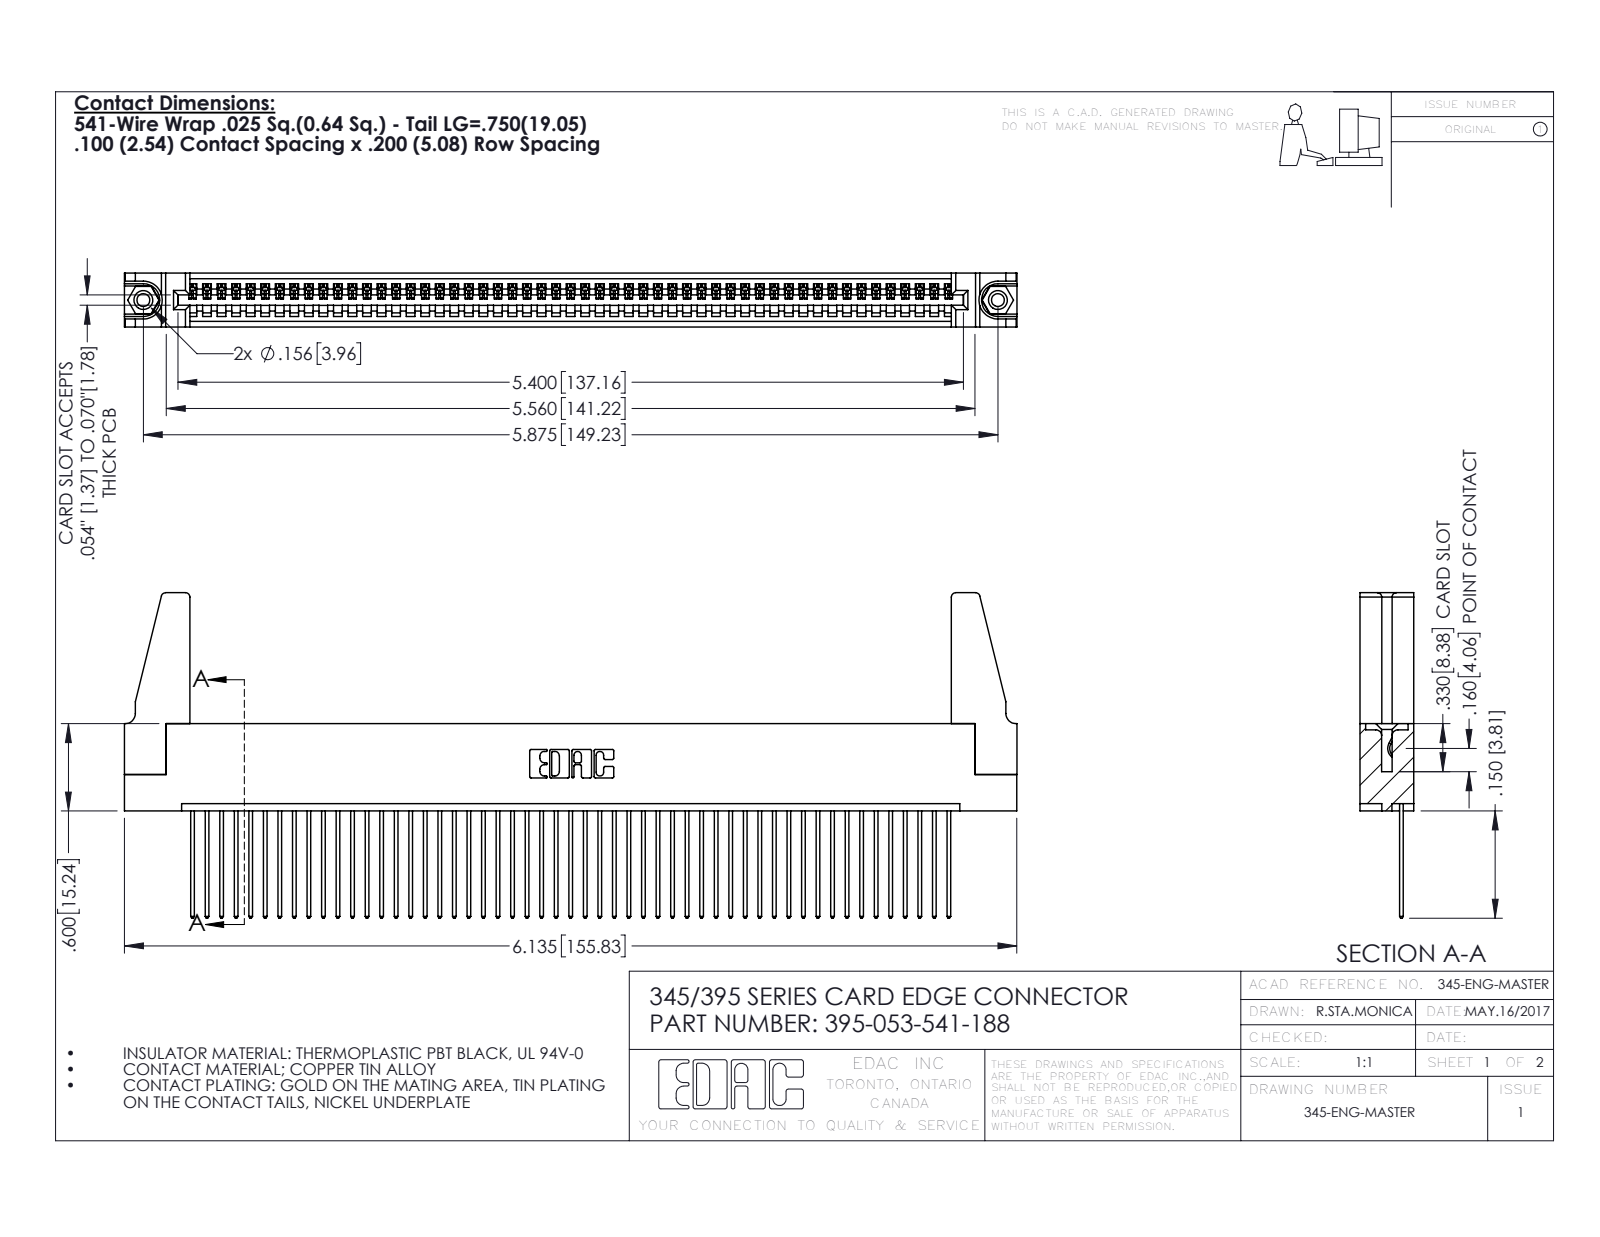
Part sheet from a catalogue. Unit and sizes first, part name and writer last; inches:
Units: inches
Overall size (bounding box): 6.136 × 2.237 × 0.37
Round holes (diameter × count): ⌀0.089 ×2, ⌀0.125 ×2, ⌀0.156 ×2, ⌀0.064 ×1
Round bosses / shafts (diameter × count): ⌀0.155 ×2
Partial cylindrical surfaces — rounded edges, fillets, slot ends (radius × count): R0.006 ×106, R0.01 ×106, R0.01 ×22, R0.03 ×8, R0.007 ×6, R0.031 ×6, R0.026 ×3, R0.031 ×2
Main face-to-face distances: 0.072, 0.298, 0.37, 0.098, 0.272, 0.025, 0.2, 0.225, 0.149, 0.072
Hole centre spacings: 0.27, 5.639, 5.875
Volume: 1.118 in³ · Surface area: 37.71 in²
Bodies: 58 solids, 3324 faces (2272 planar, 1036 cylindrical, 16 other)
Part name (STEP PRODUCT): 395-053-541-188; 345-220-078_345-220-088; 345-292-001_345-293-141; 345-250-001_345-250-001-102 (+1 more)
STEP written by: SolidWorks 2016 (CONFIG_CONTROL_DESIGN)
